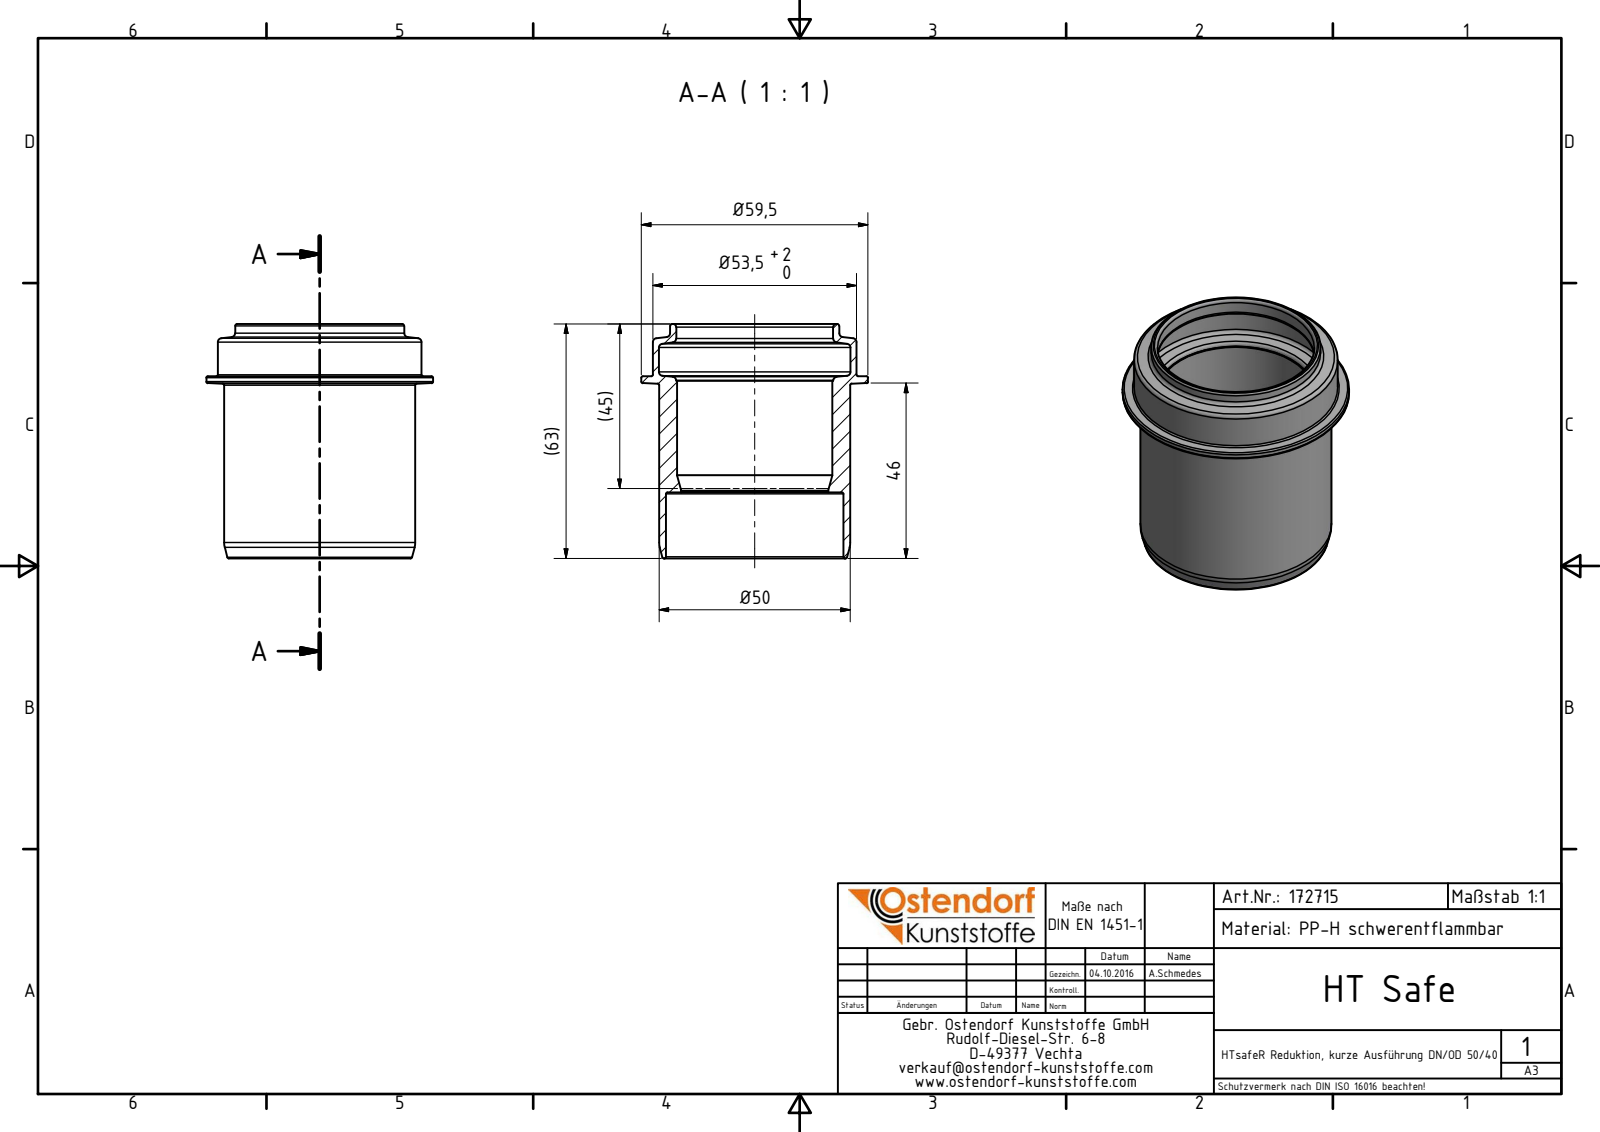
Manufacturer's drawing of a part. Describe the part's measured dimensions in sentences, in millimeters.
The part is named "172715 HTsafeR Reduktion,kurze Ausführung DN_OD 50_40". Its 3-D file was written by "Autodesk Inventor 2016 (AUTOMOTIVE_DESIGN)". It is 1 solid with 39 faces: 5 planar, 10 cylindrical and 24 other. Overall it measures 61.5 by 59.5 by 59.5 millimeters. Its volume is 31 095 cubic millimeters and its surface area 21 730 square millimeters. Round holes: 1 of diameter 38.6, 1 of diameter 40.8, 1 of diameter 41.2, 1 of diameter 46.6, 1 of diameter 50.3. Round bosses or shafts: 1 of diameter 59.5, 1 of diameter 53.5, 1 of diameter 50.2, 1 of diameter 44.4. The main face-to-face distances are 30.5, 44.2, 13.7, 29.3, 1.2, 14.9, 17.3, 46.6, 47.8, 61.5.
